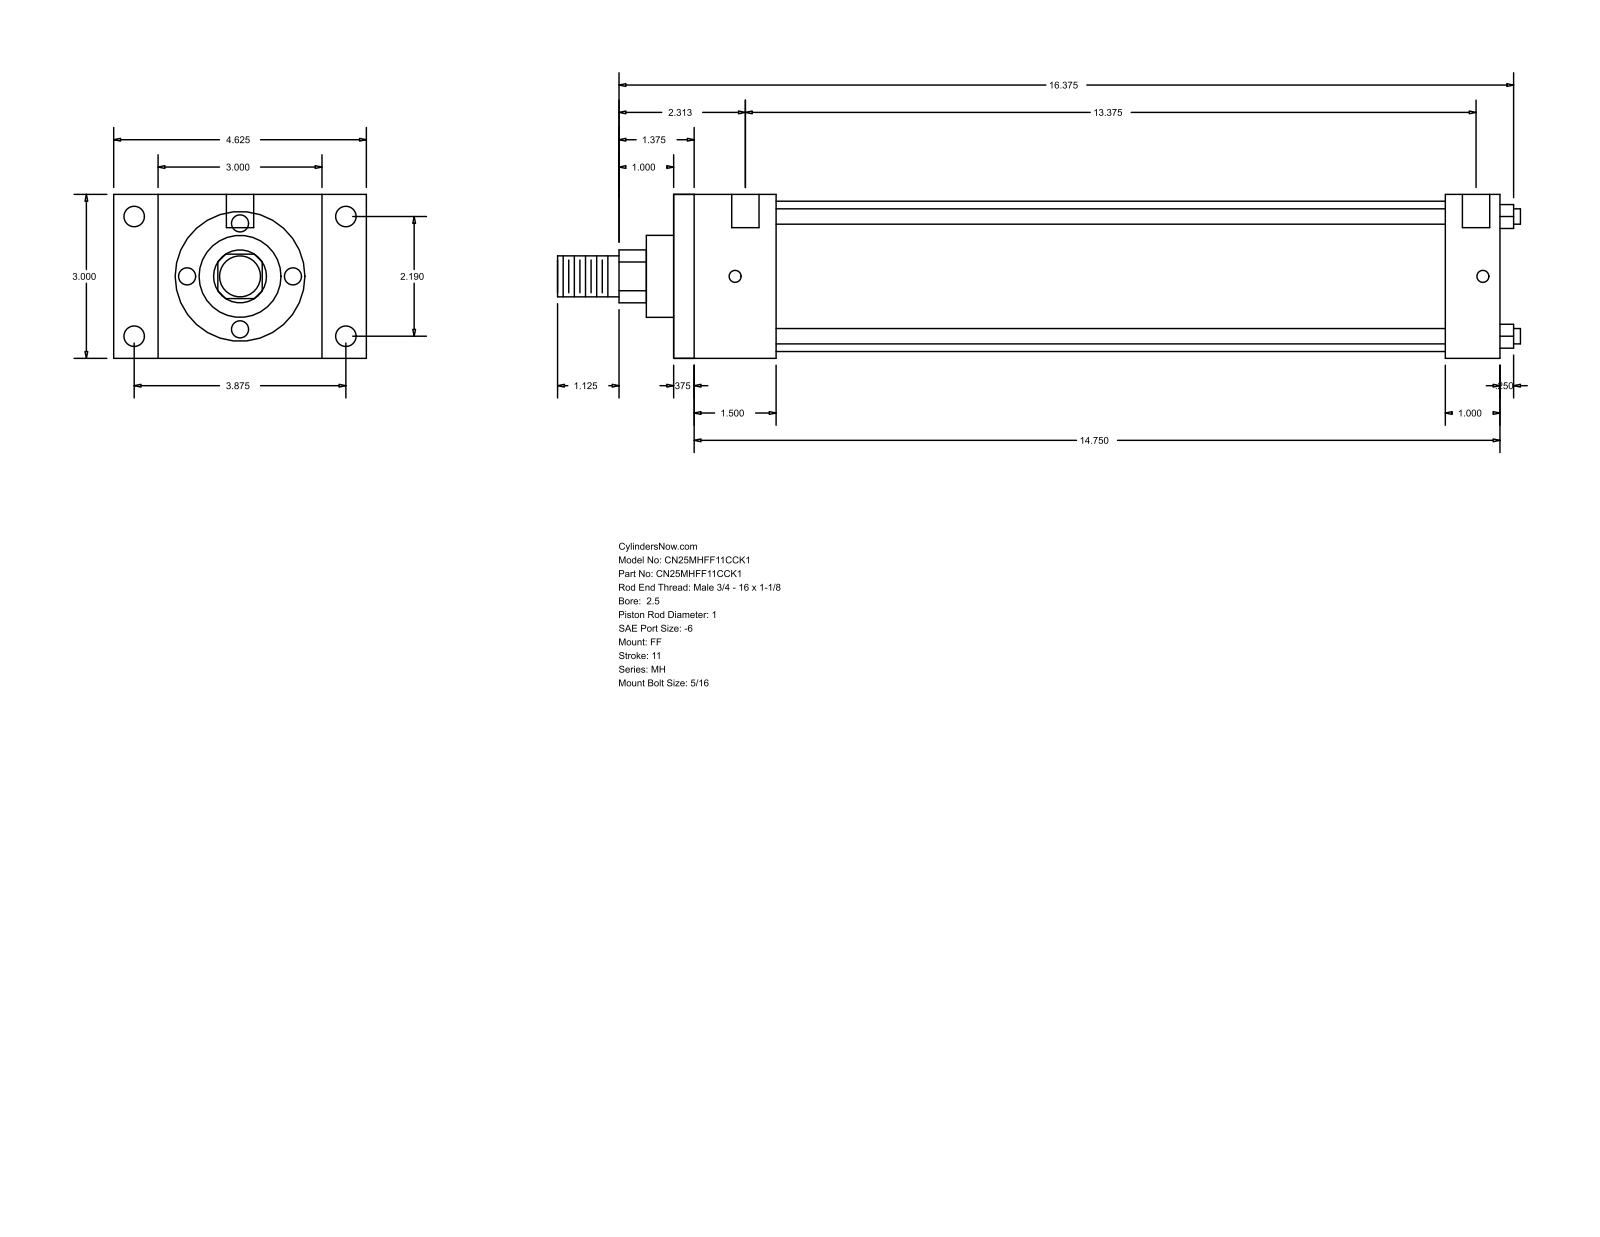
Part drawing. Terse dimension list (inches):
name: MH_FF__0250_1
written by: GSSL Pune (CONFIG_CONTROL_DESIGN)
unit: in
bodies: 0 solids, 92 faces (64 planar, 28 cylindrical, 0 other)
size: 17.625 × 4.625 × 3
holes: 4× ⌀0.219, 4× ⌀0.375, 2× ⌀0.5
bosses: 4× ⌀0.281, 1× ⌀2.75, 1× ⌀1.5, 1× ⌀1, 1× ⌀0.75
rounds: 1× R0.484
face distances: 3, 15.125, 14.75, 0.375, 1, 1.875, 14.125, 1.5, 13.75, 12.25
hole spacings: 2.19, 3.875, 4.451, 13.687, 0.125, 0.187, 13.375, 13.5
